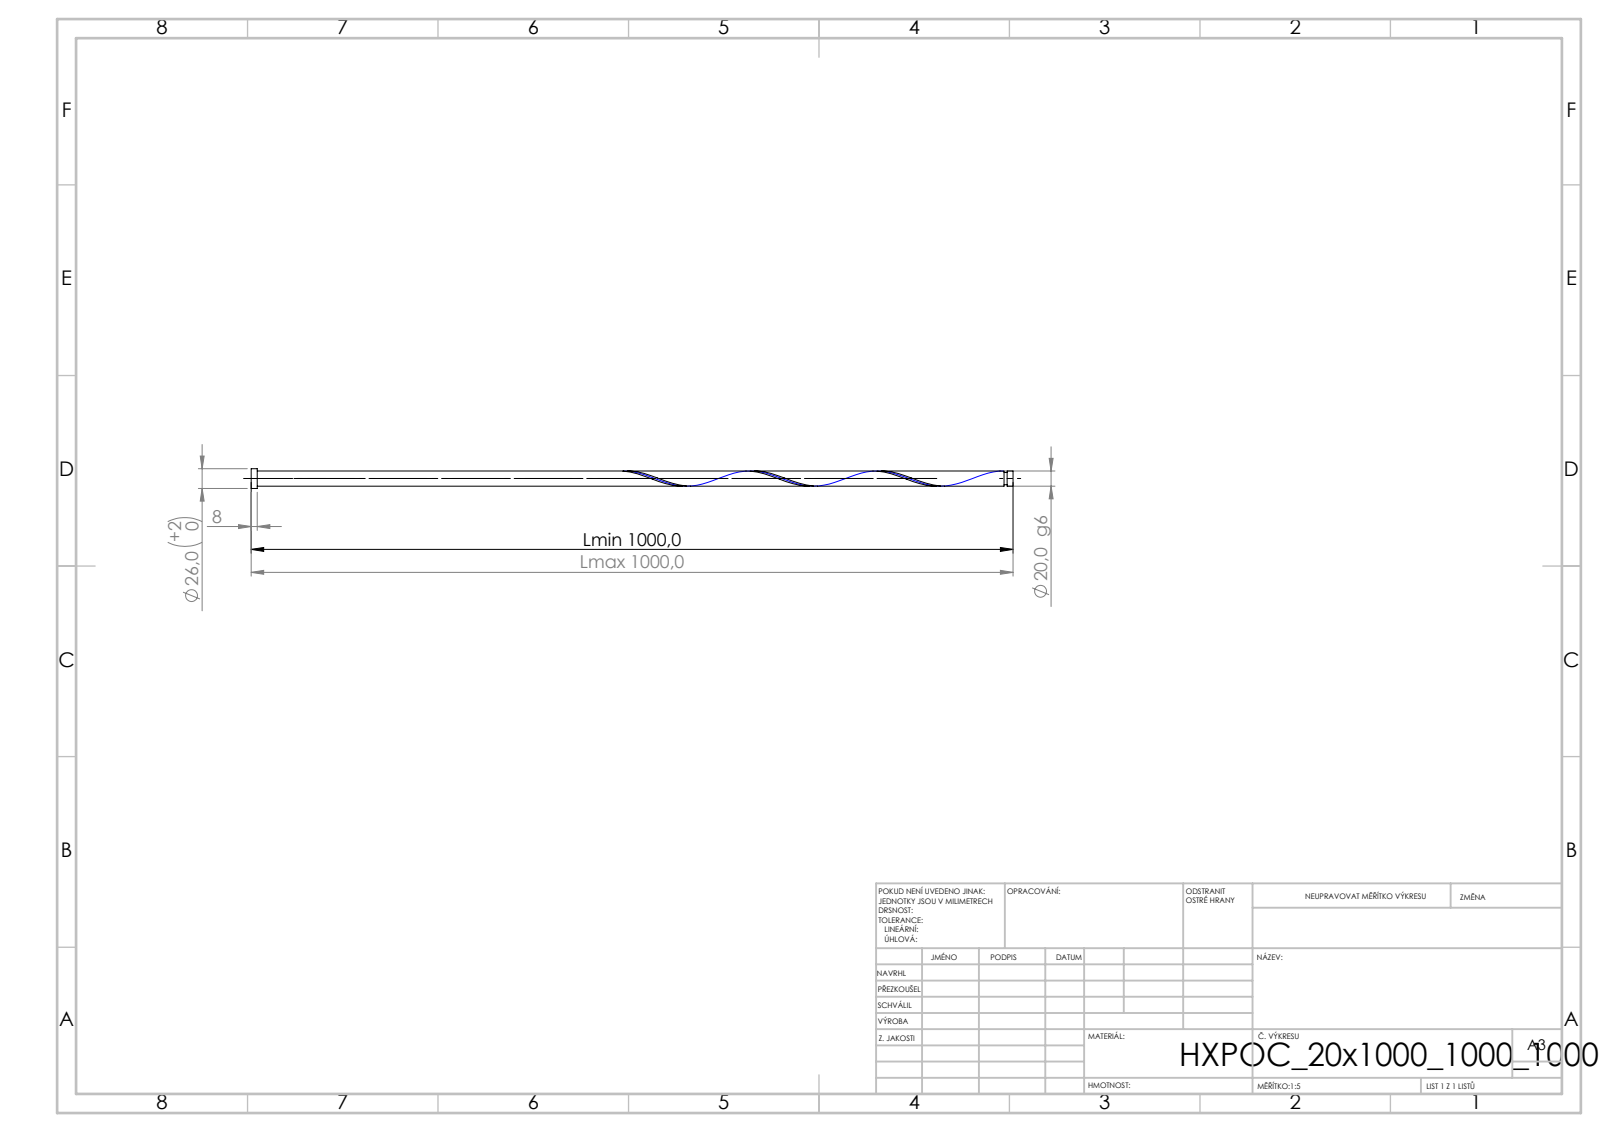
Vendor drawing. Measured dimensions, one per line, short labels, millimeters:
written by: SolidWorks 2019 (CONFIG_CONTROL_DESIGN)
unit: mm
bodies: 1 solid, 21 faces (6 planar, 14 cylindrical, 1 other)
size: 1000 × 26 × 26
volume: 312 434 mm³; area: 65 254 mm²
bosses: 1× ⌀26, 1× ⌀20, 1× ⌀16
face distances: 1000, 8, 992, 992.25, 984.25, 7.75, 988.25, 980.25, 4, 11.75
